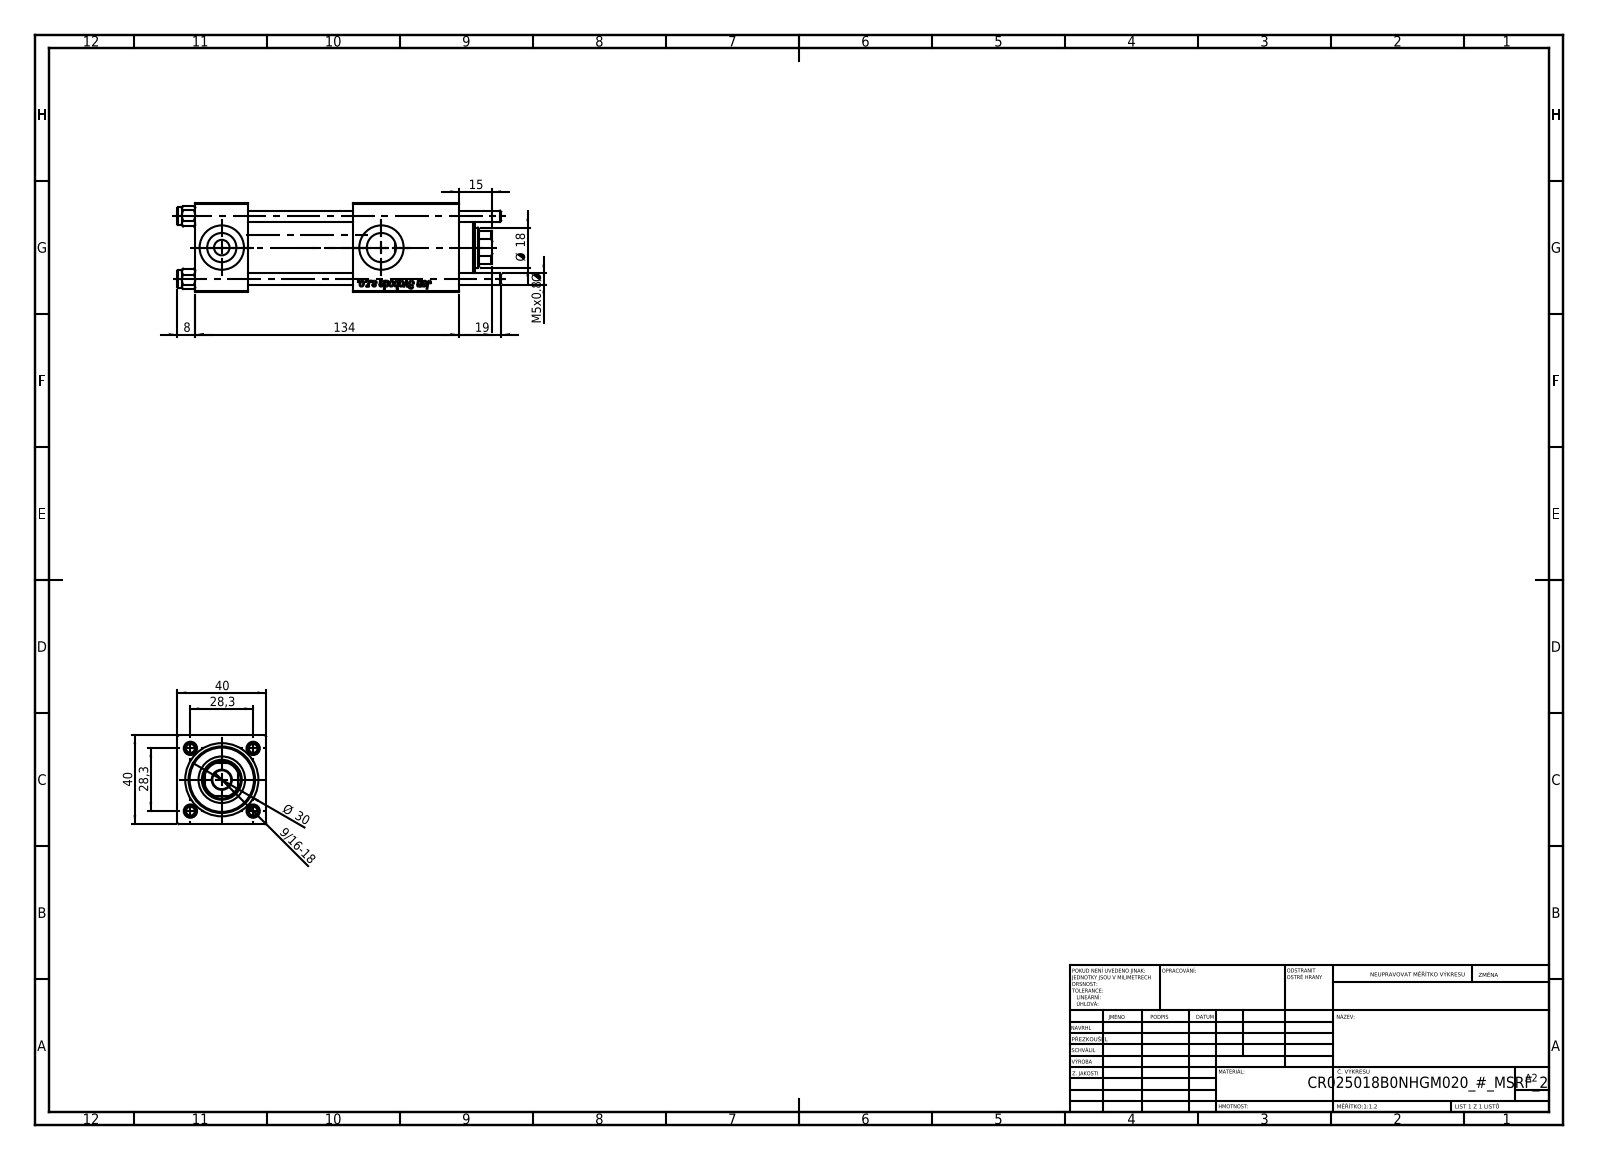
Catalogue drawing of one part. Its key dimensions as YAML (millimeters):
part_name: "NUT_M5_B; V215_VC_A; V215CR_VCP_B; V215CR_B-1 (+1 more)"
step_written_by: "SolidWorks 2019 (CONFIG_CONTROL_DESIGN)"
units: millimeters
bodies: {solids: 11, faces: 1152, planar: 428, cylindrical: 76, other: 648}
overall_size: [146, 40, 40]
volume: 152491
surface_area: 60895
round_holes:
  - {diameter: 5, count: 4}
  - {diameter: 20, count: 3}
  - {diameter: 7, count: 2}
  - {diameter: 13.16, count: 2}
  - {diameter: 8.5, count: 1}
  - {diameter: 18, count: 1}
  - {diameter: 21, count: 1}
  - {diameter: 25, count: 1}
  - {diameter: 30, count: 1}
round_bosses_or_shafts:
  - {diameter: 8, count: 4}
  - {diameter: 31, count: 1}
partial_cylinders:
  - {radius: 8.5, count: 1}
face_to_face_distances: [40, 24, 71, 47, 90.3, 66.3, 19.3, 119, 95, 48]
hole_center_spacings: [20.01, 28.3, 40.02, 72]
